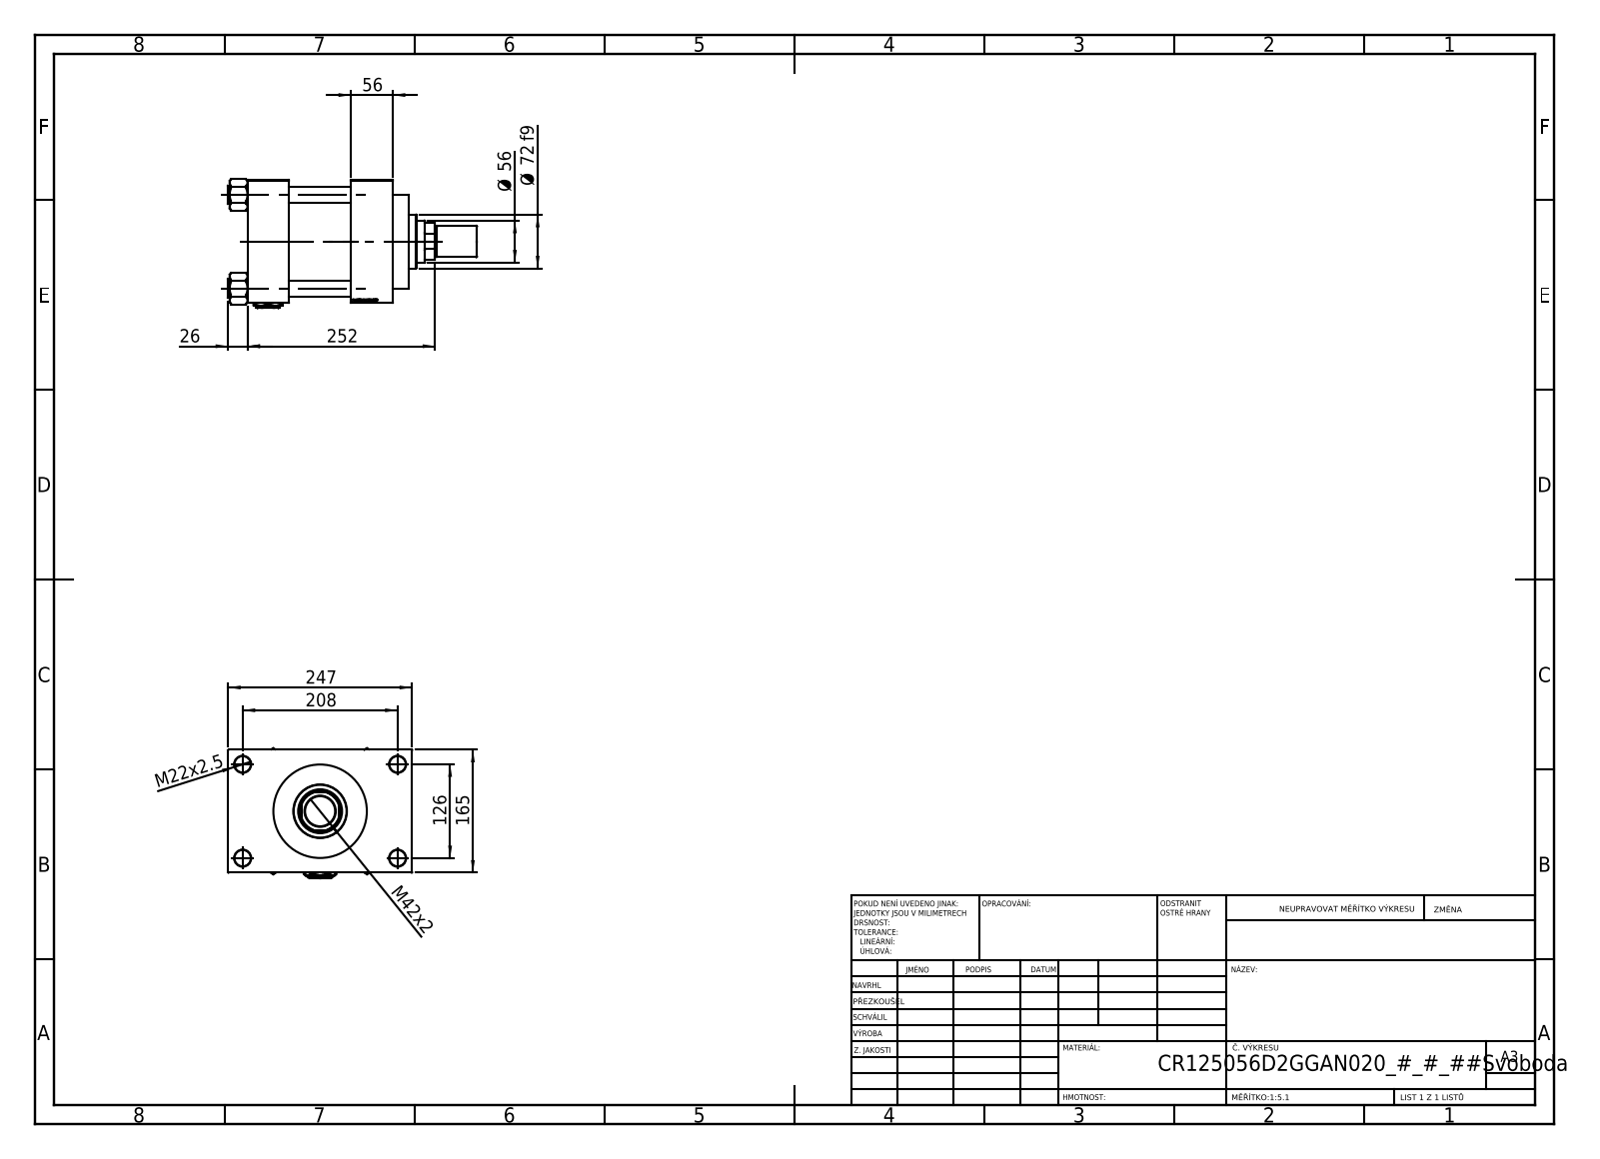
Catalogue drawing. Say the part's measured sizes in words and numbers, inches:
The part is named "ROD_END_AH; NUT_M5_D; V215CR_D_TYCINKA; V215_VC_A (+3 more)". Its 3-D file was written by "SolidWorks 2019 (CONFIG_CONTROL_DESIGN)". It is 13 solids with 1216 faces: 572 planar, 98 cylindrical and 546 other. Overall it measures 13.15 by 9.724 by 6.853 inches. Its volume is 307 cubic inches and its surface area 846.4 square inches. Round holes: 8 of diameter 0.866, 2 of diameter 0.276, 2 of diameter 1.269, 2 of diameter 1.772, 1 of diameter 1.594, 1 of diameter 2.205, 1 of diameter 2.323, 1 of diameter 3.78, 1 of diameter 4.921, 1 of diameter 4.941. Round bosses or shafts: 4 of diameter 0.984, 1 of diameter 5.157, 1 of diameter 2.835, 1 of diameter 1.654, 1 of diameter 1.575. Partial cylindrical surfaces (rounded edges, fillets, slot ends): 1 of radius 1.063. The main face-to-face distances are 6.496, 3.307, 2.165, 5.472, 2.205, 7.677, 5.512, 1.614, 8.11, 6.84. The hole center spacings are 1.616, 3.505, 4.787, 4.957, 5.215, 6.573, 8.233, 4.961.
